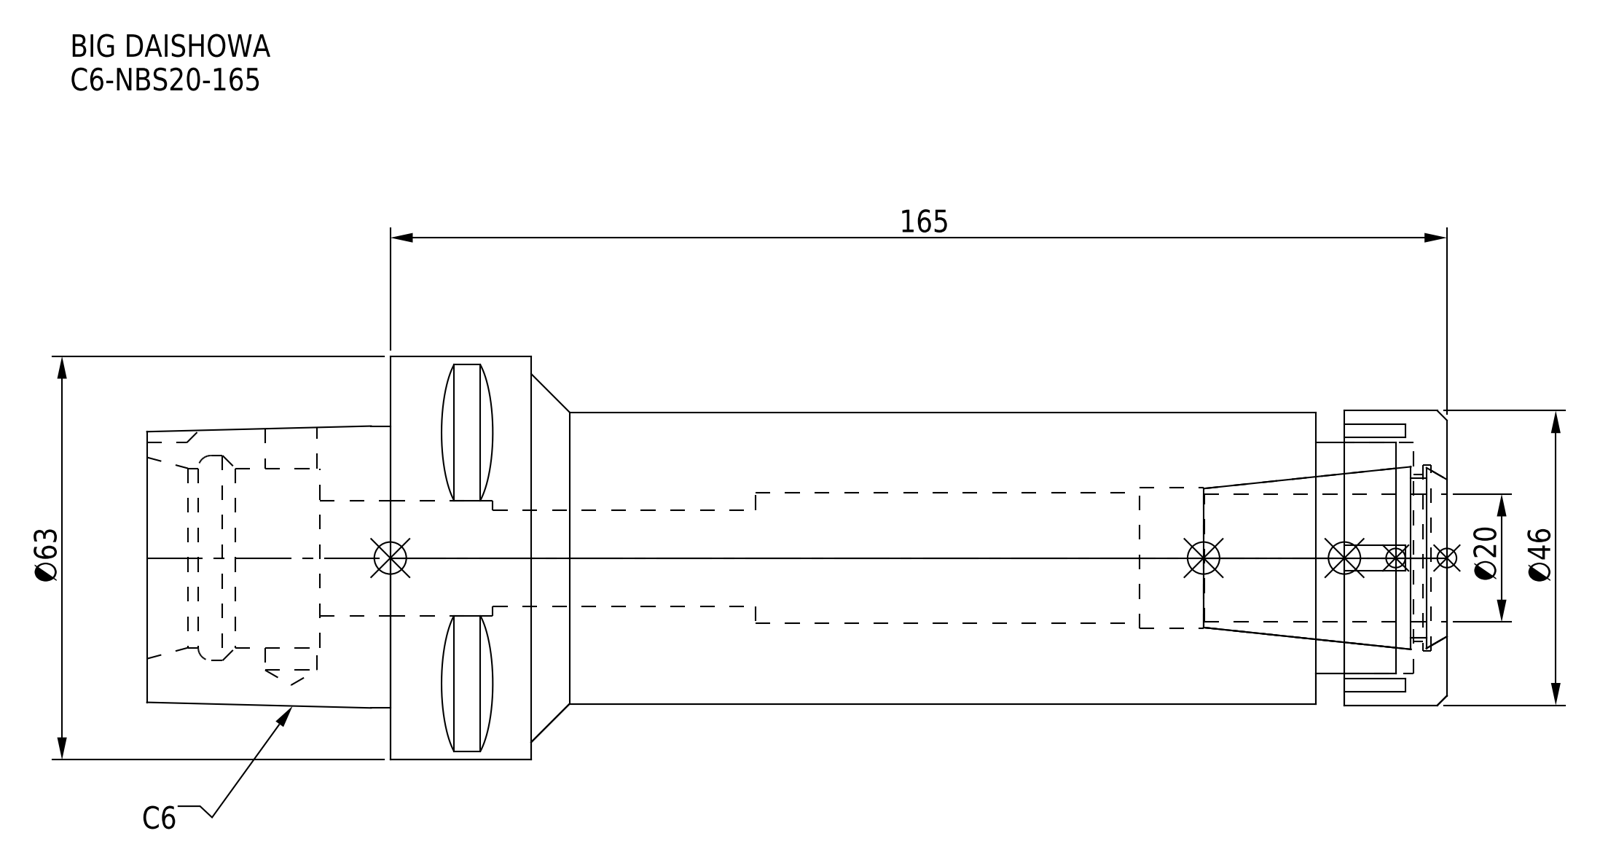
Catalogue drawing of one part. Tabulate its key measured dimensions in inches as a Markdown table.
| quantity | value |
| --- | --- |
| part name | DXF_TEMP_ASSY_ASM_4_ASM.stp; C6-NBS20-165.stp; C6-NBS20-165; C6-NBS20-165_1.stp (+3 more) |
| STEP written by | SolidWorks 2019 (CONFIG_CONTROL_DESIGN) |
| units | inches |
| bodies | 2 solids, 112 faces (61 planar, 33 cylindrical, 18 other) |
| overall size | 7.992 × 2.48 × 2.48 |
| volume | 16.97 in³ |
| surface area | 83.02 in² |
| round holes (diameter × count) | 0.319 × 1, 0.591 × 1, 0.709 × 1, 0.799 × 1, 0.866 × 1, 1.024 × 1, 1.102 × 1, 1.142 × 1, 1.26 × 1, 1.417 × 1 |
| round bosses / shafts (diameter × count) | 2.48 × 1, 1.811 × 1, 1.791 × 1 |
| partial cylindrical surfaces (radius × count) | 0.197 × 1 |
| main face-to-face distances | 6.496, 0.315, 0.63, 5.866, 0.807, 5.689, 0.177, 2.362, 0.866, 5 |
